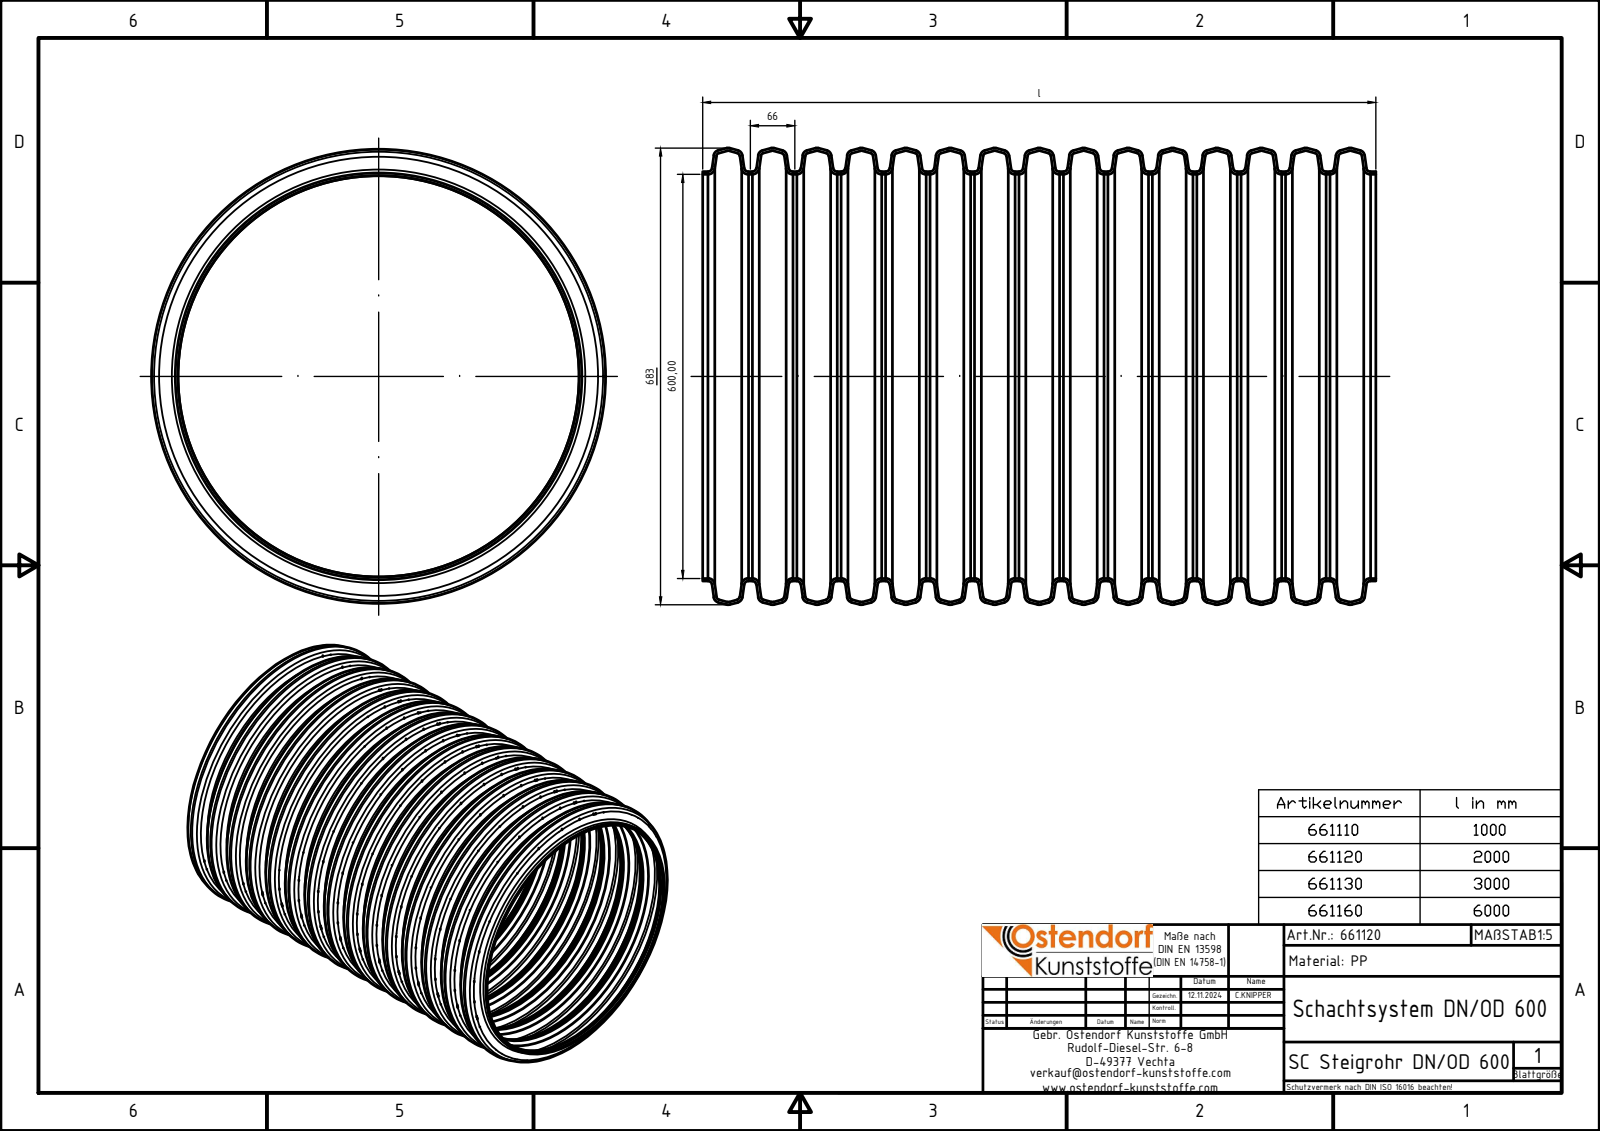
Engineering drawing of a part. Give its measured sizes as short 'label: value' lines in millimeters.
name: 661120z
written by: Autodesk Inventor 2024 (AUTOMOTIVE_DESIGN)
unit: mm
bodies: 1 solid, 604 faces (2 planar, 62 cylindrical, 540 other)
size: 2000 × 678.36 × 678.36
volume: 27 540 000 mm³; area: 13 770 000 mm²
holes: 1× ⌀600
bosses: 1× ⌀607.99
face distances: 2000
